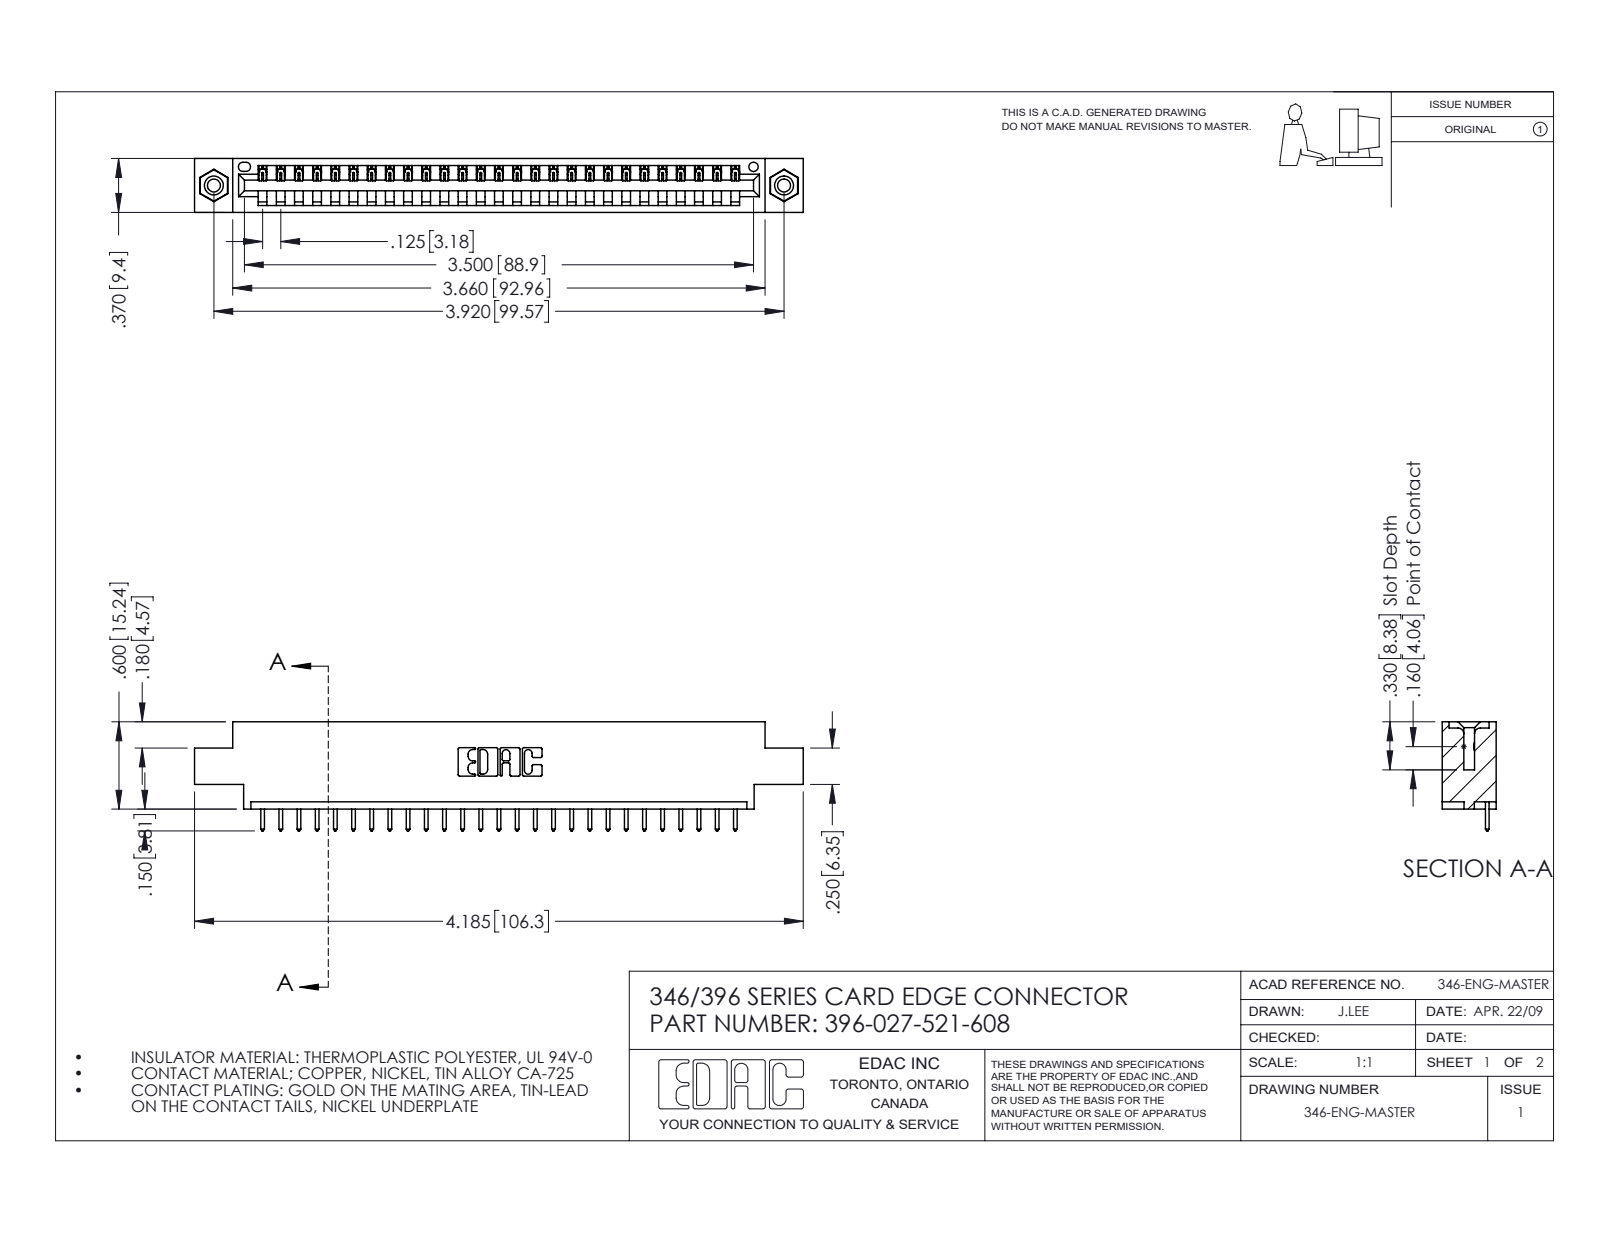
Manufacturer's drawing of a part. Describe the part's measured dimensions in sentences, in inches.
The part is named "345-292-001_345-293-121; 396-027-521-608; 346 Part_0.170 Offset - 0.156 Dia-TI; 345-250-001_345-250-003-102". Its 3-D file was written by "SolidWorks 2016 (CONFIG_CONTROL_DESIGN)". It is 30 solids with 1752 faces: 1192 planar, 544 cylindrical and 16 other. Overall it measures 4.185 by 0.75 by 0.37 inches. Its volume is 0.6 cubic inches and its surface area 18.61 square inches. Round holes: 2 of diameter 0.089, 2 of diameter 0.125, 2 of diameter 0.156, 1 of diameter 0.064. Round bosses or shafts: 2 of diameter 0.155. Partial cylindrical surfaces (rounded edges, fillets, slot ends): 54 of radius 0.006, 54 of radius 0.01, 22 of radius 0.01, 6 of radius 0.007, 6 of radius 0.031, 3 of radius 0.026, 2 of radius 0.031, 2 of radius 0.04. The main face-to-face distances are 0.048, 0.322, 0.37, 0.25, 0.072, 0.298, 0.025, 0.222, 0.148, 0.1. The hole center spacings are 0.246, 3.712, 3.92.
